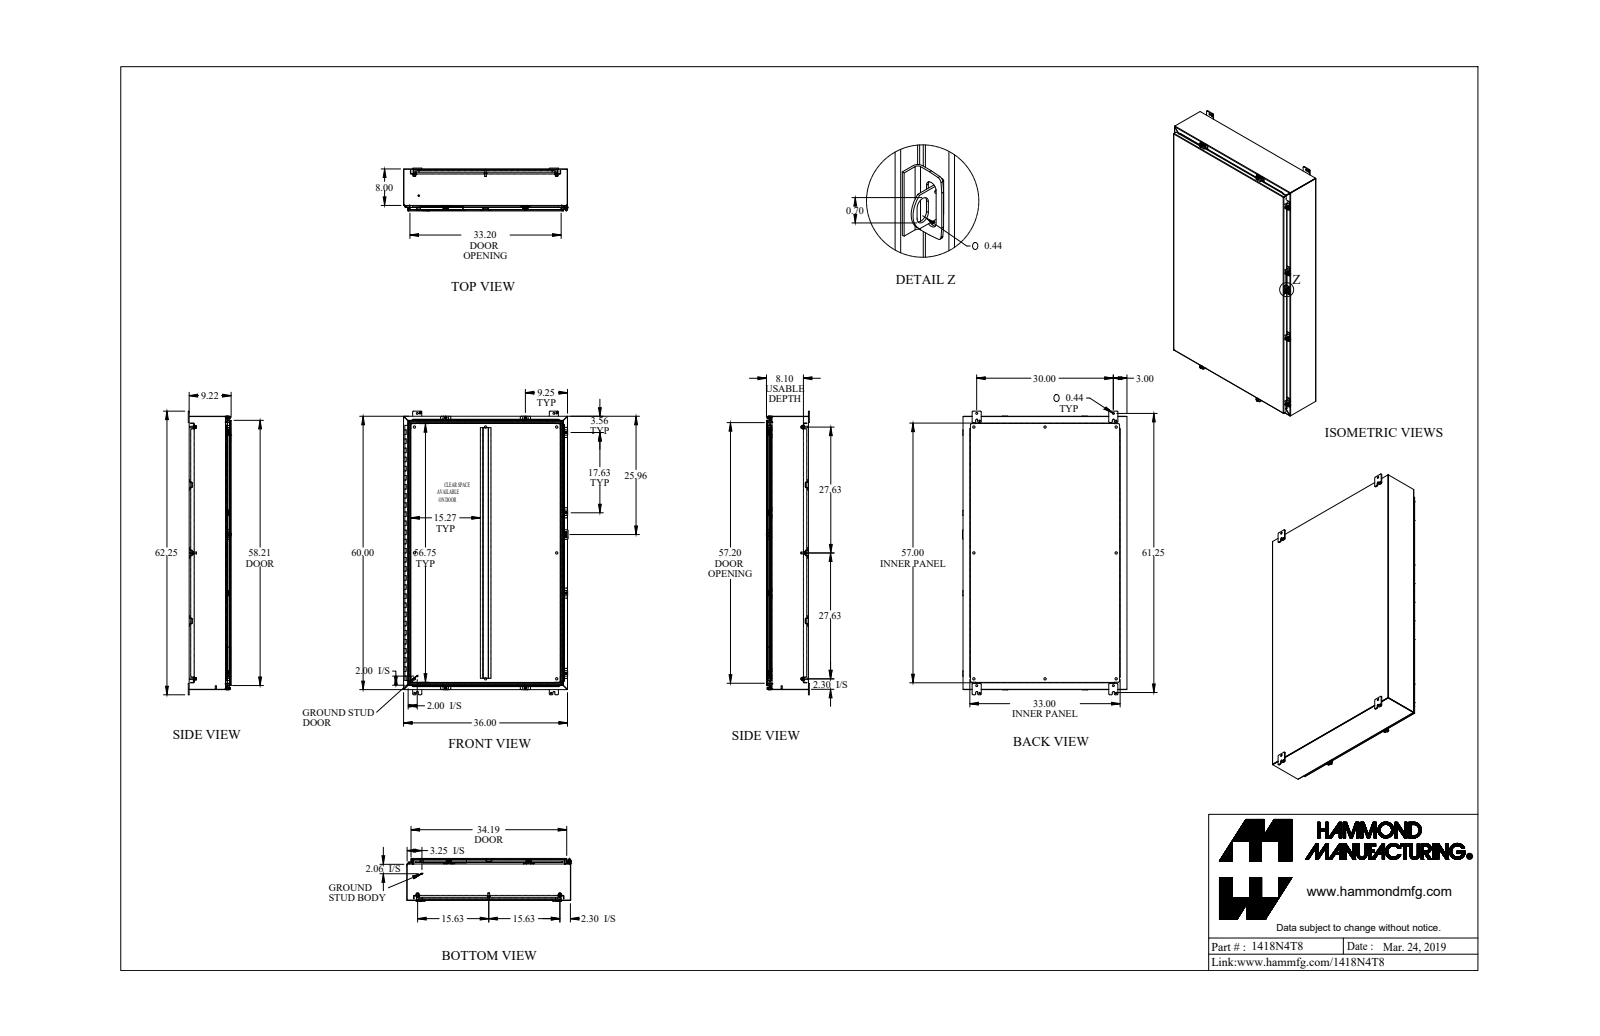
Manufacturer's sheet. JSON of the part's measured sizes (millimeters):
{"part_name": "1418N4T8", "step_written_by": "SolidWorks 2019 (AUTOMOTIVE_DESIGN)", "units": "millimeters", "bodies": {"solids": 69, "faces": 2180, "planar": 1445, "cylindrical": 635, "other": 100}, "overall_size": [1581.2, 917.6, 239.7], "volume_mm3": 11630000, "surface_area_mm2": 11890000, "round_holes": [[5.4, 8], [6.7, 8], [9.5, 8], [12.7, 8], [7.8, 4], [8, 4], [11.1, 4], [11.3, 4], [3.2, 1], [4.7, 1]], "round_bosses_or_shafts": [[16.5, 8], [12.7, 8], [9.9, 8], [9.5, 8], [8.4, 8], [6.2, 8], [25.4, 4], [7.1, 2]], "partial_cylinders_radius": [[6.4, 48], [1.2, 39], [3.6, 39], [4.8, 36], [0.9, 22], [2.7, 22], [2.9, 16], [3.6, 16]], "face_to_face_distances": [1.8, 232.2, 230.4, 234.1, 2.4, 206, 204.2, 26.2, 28, 208.4], "hole_center_spacings": [182.8, 396.9, 621.5, 1403.4, 1458.4, 701.7, 793.8, 1467.7]}
